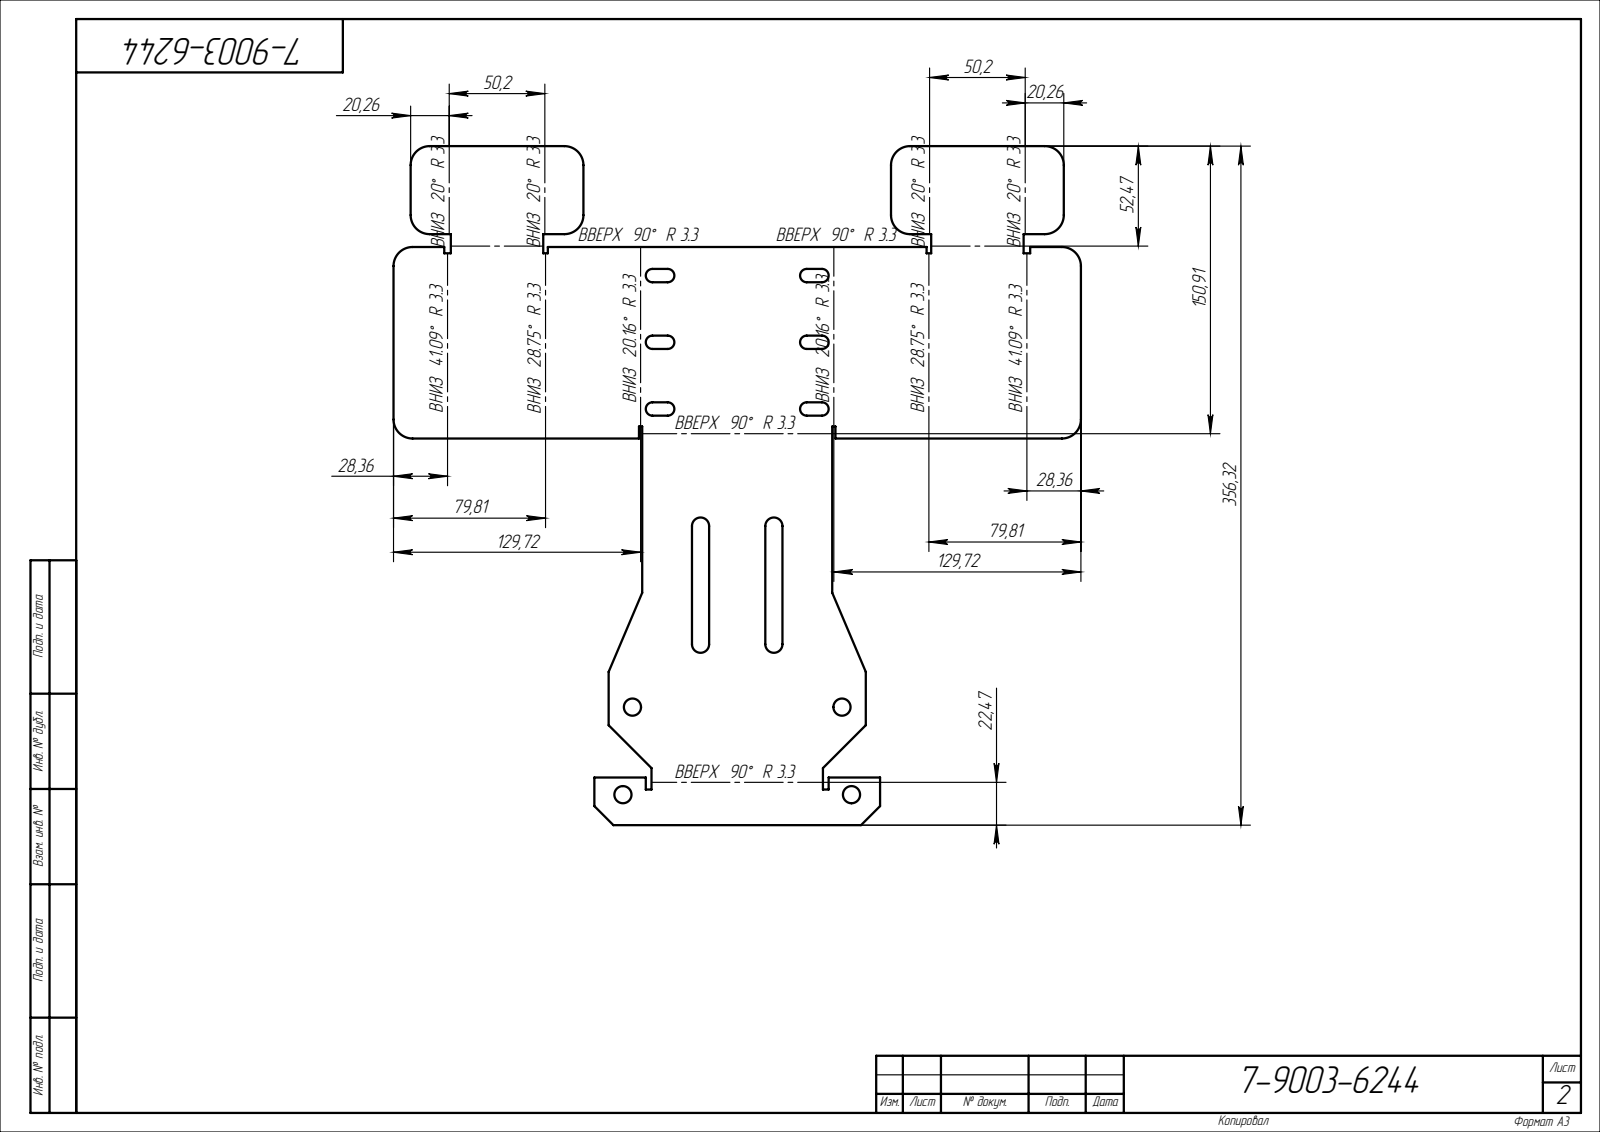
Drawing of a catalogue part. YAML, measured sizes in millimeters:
part_name: "7-9003-6244 Основание неподвижной каретки"
step_written_by: "SolidWorks 2021 (AUTOMOTIVE_DESIGN)"
units: millimeters
bodies: {solids: 1, faces: 202, planar: 130, cylindrical: 72, other: 0}
overall_size: [360.16, 271, 110.34]
volume: 198708
surface_area: 139985
round_holes:
  - {diameter: 9, count: 4}
partial_cylinders:
  - {radius: 3.3, count: 14}
  - {radius: 6.3, count: 14}
  - {radius: 3.5, count: 12}
  - {radius: 10, count: 10}
  - {radius: 4.5, count: 4}
face_to_face_distances: [3, 100.5, 185, 97.5, 263, 3.01, 103.5, 188, 182, 266]
hole_center_spacings: [110, 120]
